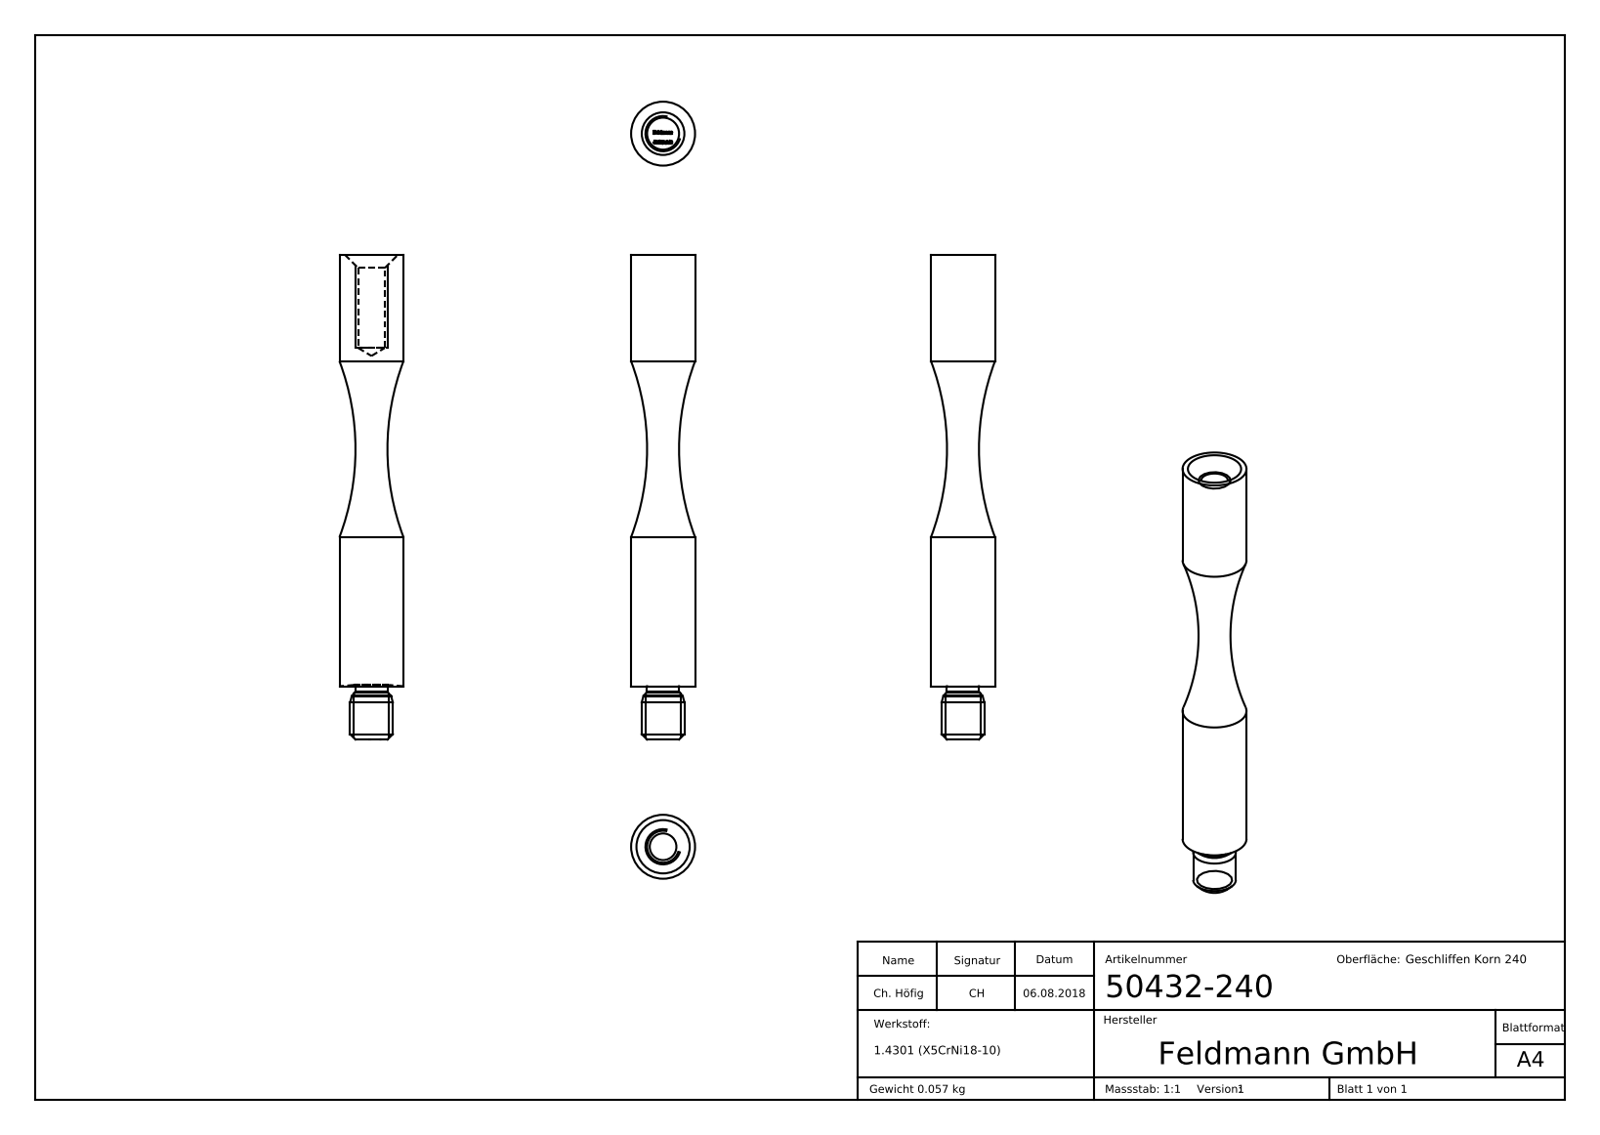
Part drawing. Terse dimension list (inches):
name: 50432-240
written by: SolidWorks 2015 (CONFIG_CONTROL_DESIGN)
unit: in
bodies: 1 solid, 265 faces (131 planar, 10 cylindrical, 124 other)
size: 3.583 × 0.472 × 0.472
volume: 0.438 in³; area: 5.281 in²
holes: 1× ⌀0.197
bosses: 1× ⌀0.472, 1× ⌀0.315, 1× ⌀0.236
face distances: 3.583, 3.579, 0.074, 0.047, 0.026, 0.072, 0.081, 0.057, 0.053, 0.069
